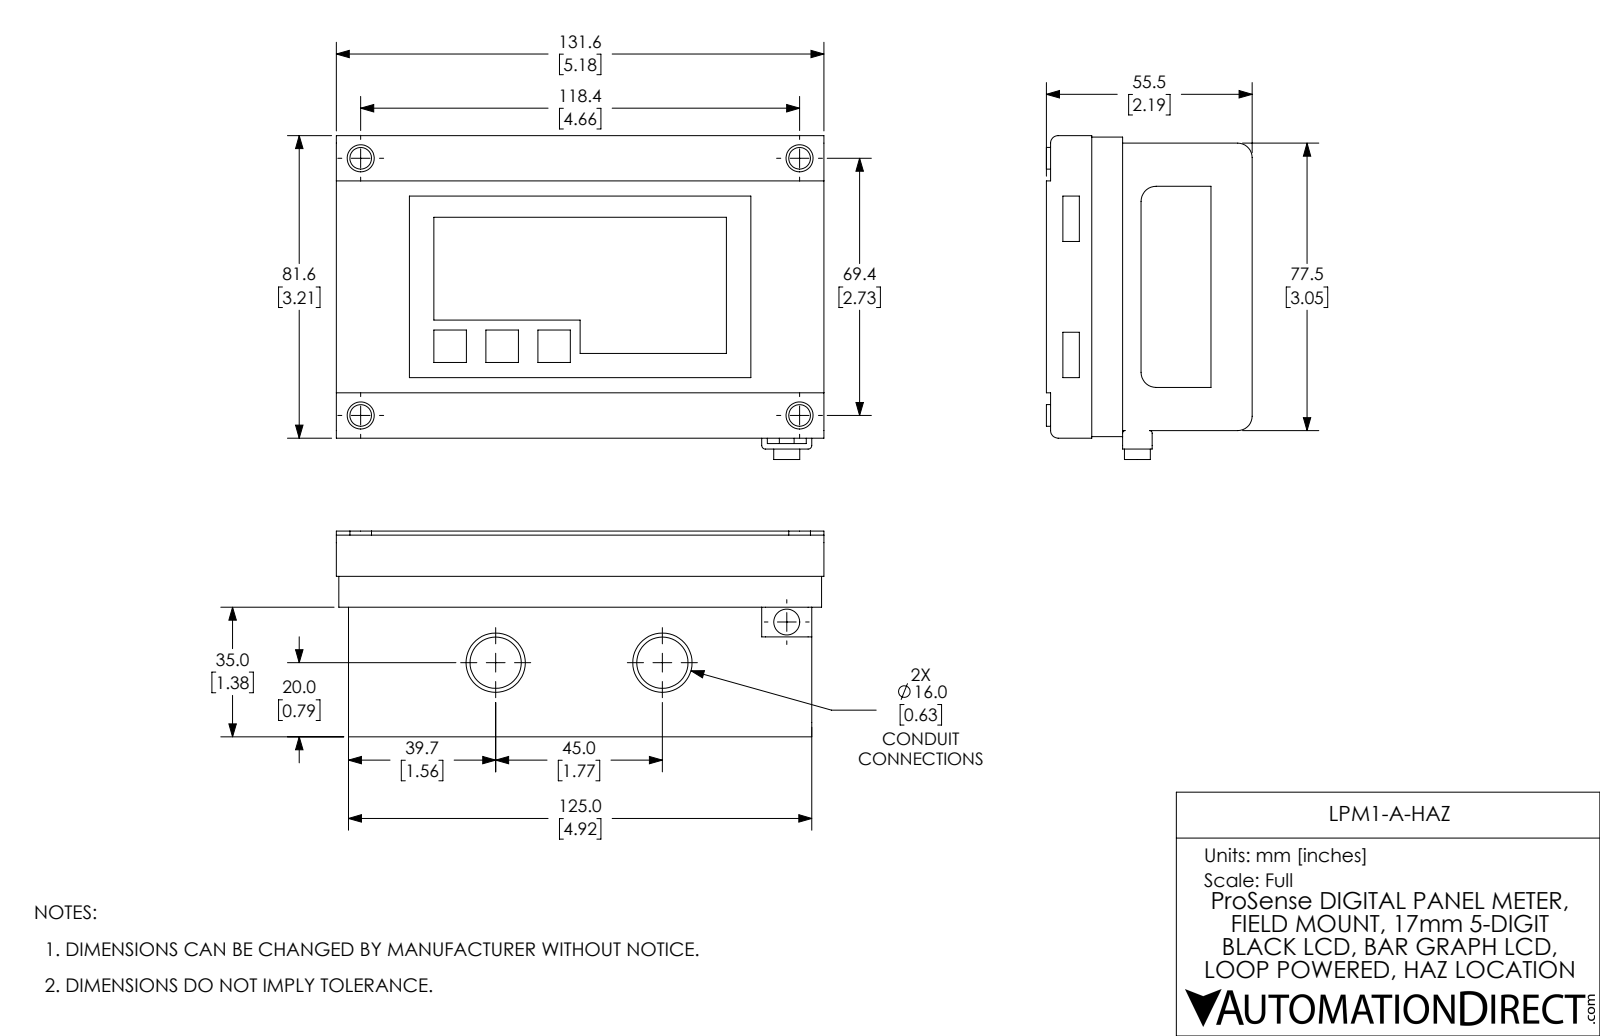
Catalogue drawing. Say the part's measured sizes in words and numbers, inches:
The part is named "LPM1-A-HAZ". Its 3-D file was written by "SolidWorks 2017 (AUTOMOTIVE_DESIGN)". It is 1 solid with 148 faces: 100 planar, 40 cylindrical and 8 other. Overall it measures 5.181 by 3.439 by 2.185 inches. Its volume is 32.14 cubic inches and its surface area 76.46 square inches. Round holes: 4 of diameter 0.288, 2 of diameter 0.545, 1 of diameter 0.165. Round bosses or shafts: 4 of diameter 0.23, 1 of diameter 0.276, 1 of diameter 0.157. Partial cylindrical surfaces (rounded edges, fillets, slot ends): 2 of radius 0.028, 2 of radius 0.039, 2 of radius 0.08, 2 of radius 0.153, 2 of radius 0.161. The main face-to-face distances are 3.052, 0.175, 2.185, 0.131, 2.01, 2.141, 0.044, 0.08, 3.132, 0.016. The hole center spacings are 2.731, 4.663, 5.404, 1.39, 1.772, 3.123.
